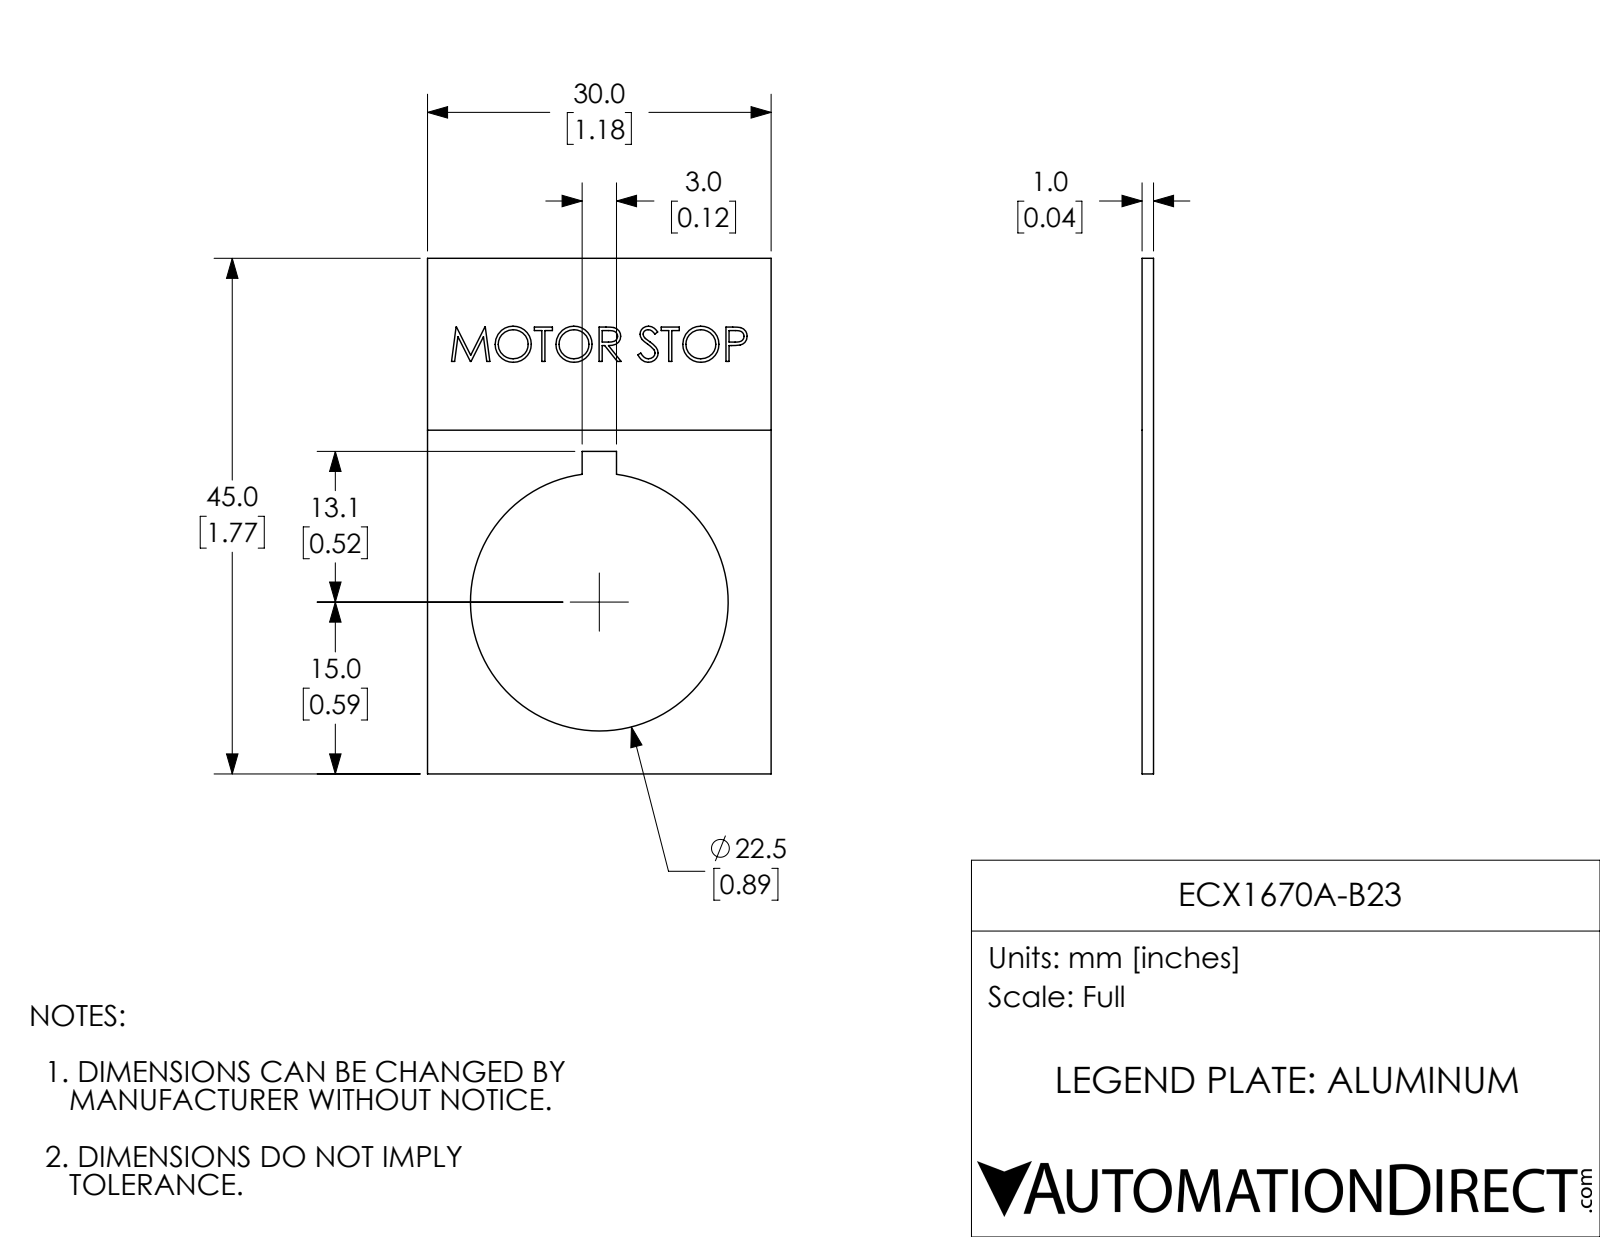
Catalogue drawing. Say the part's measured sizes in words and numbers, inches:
The part is named "ECX1670A-B23". Its 3-D file was written by "SolidWorks 2017 (AUTOMOTIVE_DESIGN)". It is 1 solid with 127 faces: 74 planar, 3 cylindrical and 50 other. Overall it measures 1.772 by 1.181 by 0.039 inches. Its volume is 0.058 cubic inches and its surface area 3.288 square inches. Round holes: 1 of diameter 0.886. The main face-to-face distances are 0.039, 1.181, 1.772, 0.038, 0.531, 0.65, 1.108, 0.663, 0.118, 0.436.
